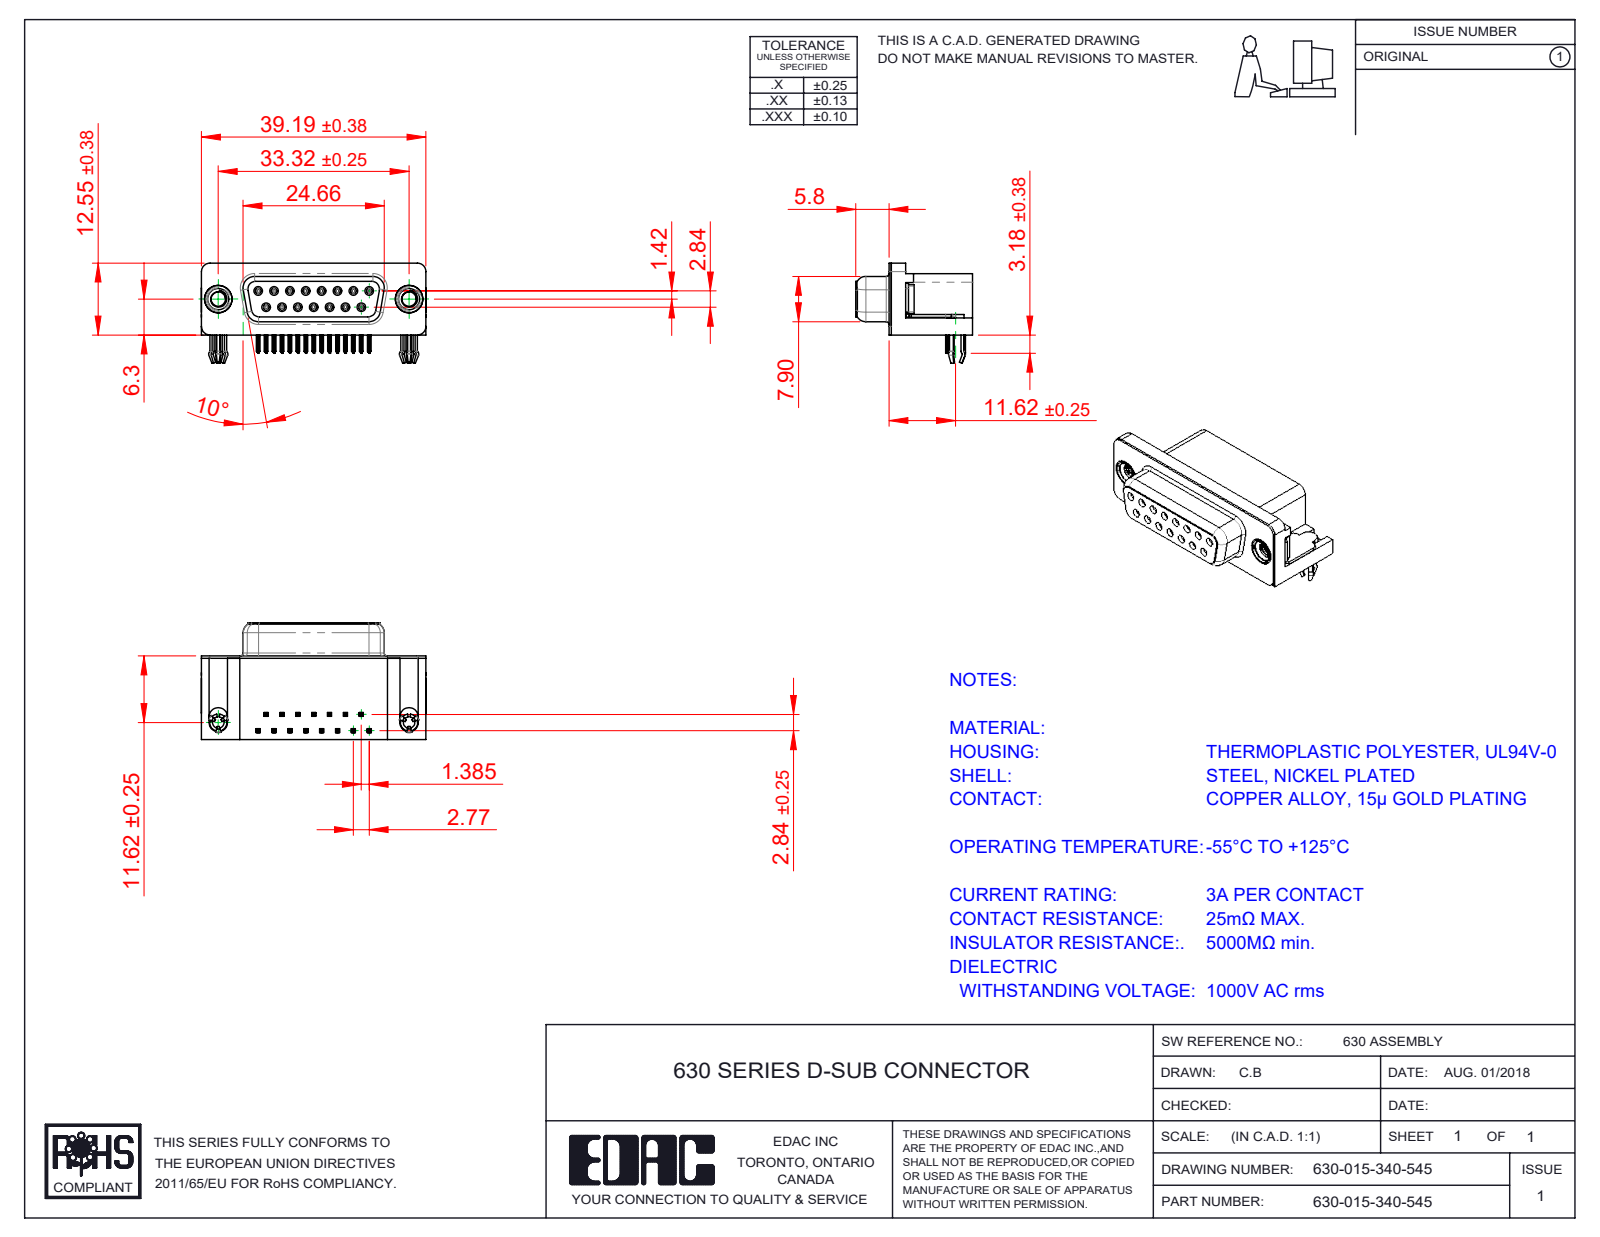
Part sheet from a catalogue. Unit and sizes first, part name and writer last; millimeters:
Units: millimetres
Overall size (bounding box): 39.22 × 20.4 × 17.48
Round holes (diameter × count): ⌀0.8 ×15, ⌀0.9 ×15, ⌀2 ×2, ⌀2.5 ×2, ⌀4 ×2, ⌀4.8 ×2, ⌀5 ×2
Round bosses / shafts (diameter × count): ⌀1.2 ×15, ⌀4.9 ×2, ⌀4.75 ×2, ⌀3.9 ×2, ⌀3 ×2
Partial cylindrical surfaces — rounded edges, fillets, slot ends (radius × count): R0.1 ×120, R0.15 ×60, R0.35 ×30, R1 ×18, R0.34 ×15, R0.25 ×12, R1.35 ×8, R1.5 ×8
Main face-to-face distances: 0.4, 14.2, 10.35, 6.2, 2.73, 14.6, 2.9, 3.18, 6.65, 9.38
Hole centre spacings: 3.16, 2.77, 5.54, 5.03, 5.04, 7.48, 7.49, 8.31
Volume: 5 863 mm³ · Surface area: 7 263 mm²
Bodies: 21 solids, 2529 faces (1110 planar, 615 cylindrical, 804 other)
Part name (STEP PRODUCT): 630 3 Prong Board Lock; 630 Shell_15 Socket; 630 Contact Top; 630 M3 Threaded Rivet (+3 more)
STEP written by: SolidWorks 2020 (CONFIG_CONTROL_DESIGN)
